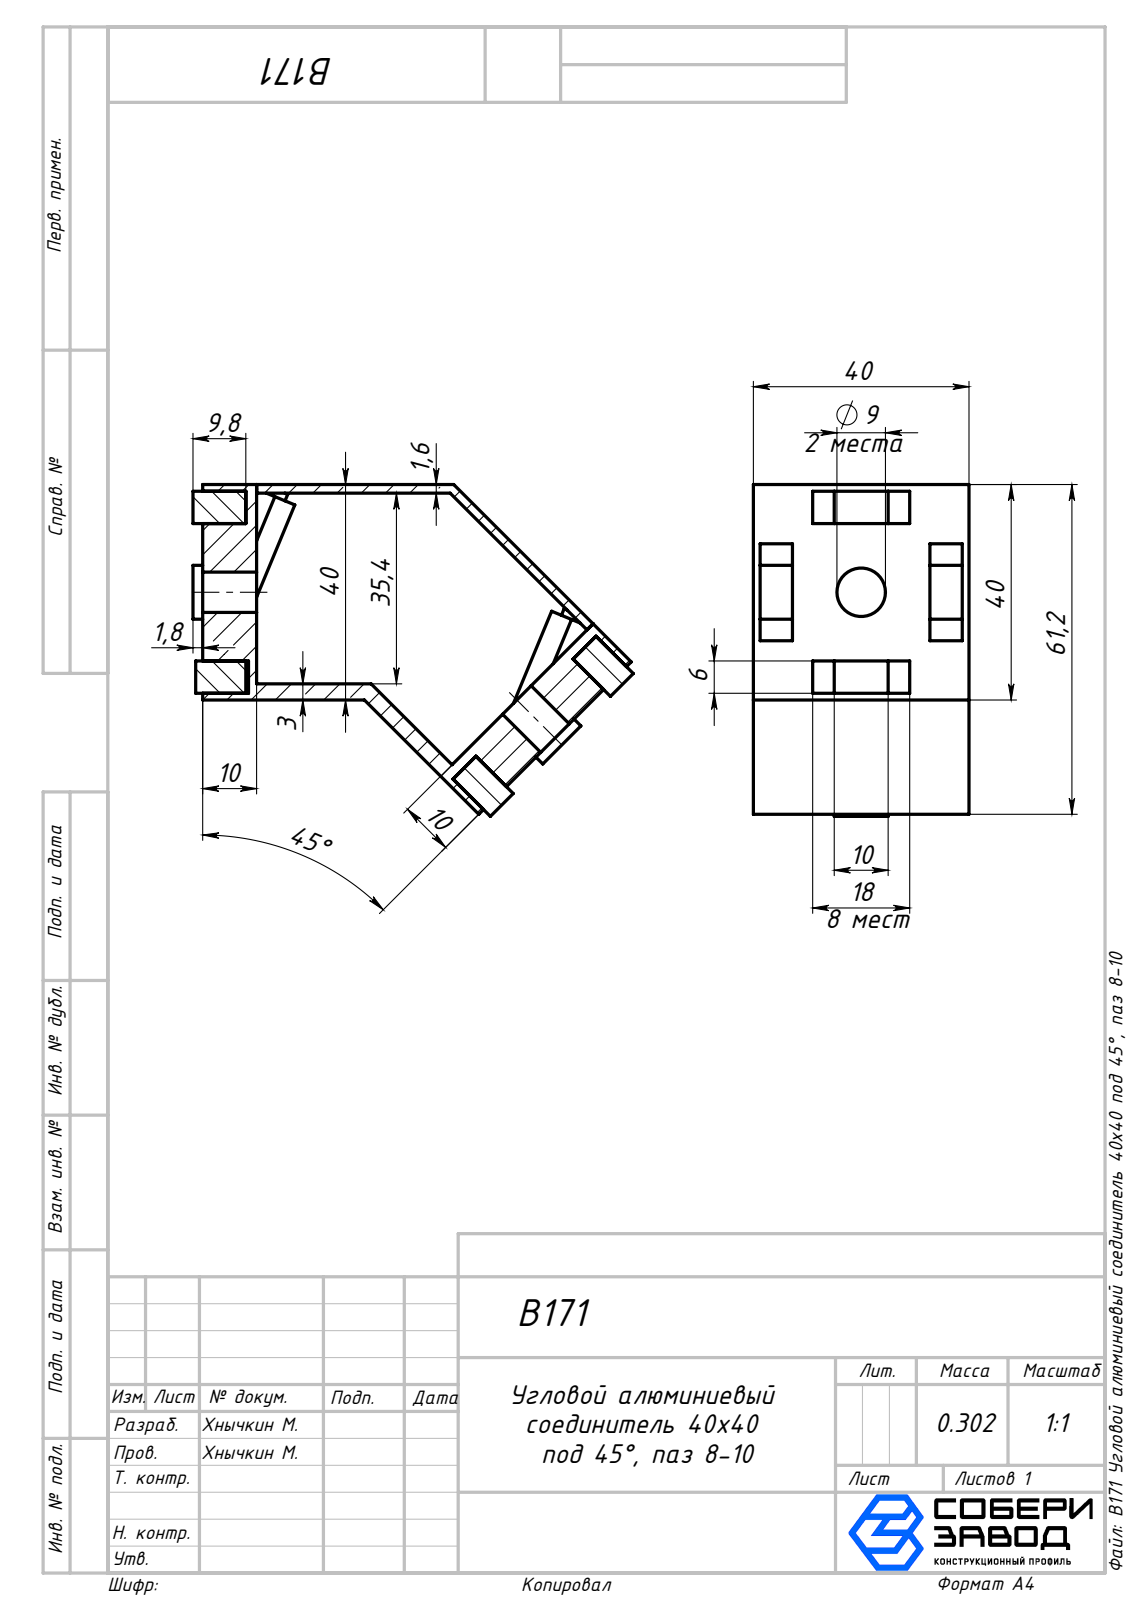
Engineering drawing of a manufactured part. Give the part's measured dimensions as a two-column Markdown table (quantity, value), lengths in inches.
| quantity | value |
| --- | --- |
| part name | B171 Крышка_00; B171 Внтурнний сухарь_00; B171 Корпус_00; B171 Угловой алюминиевый соединитель 40х40 под 45°, паз 8-10 |
| STEP written by | SolidWorks 2025 (AUTOMOTIVE_DESIGN) |
| units | inches |
| bodies | 10 solids, 254 faces (230 planar, 24 cylindrical, 0 other) |
| overall size | 3.216 × 2.425 × 1.772 |
| volume | 3.992 in³ |
| surface area | 57.13 in² |
| round holes (diameter × count) | 0.197 × 4, 0.354 × 2 |
| round bosses / shafts (diameter × count) | 0.177 × 4 |
| partial cylindrical surfaces (radius × count) | 0.157 × 4 |
| main face-to-face distances | 0.177, 1.594, 1.772, 0.063, 0.118, 0.394, 1.24, 1.417, 0.236, 0.148 |
| hole center spacings | 1.181, 2.362, 2.641 |
